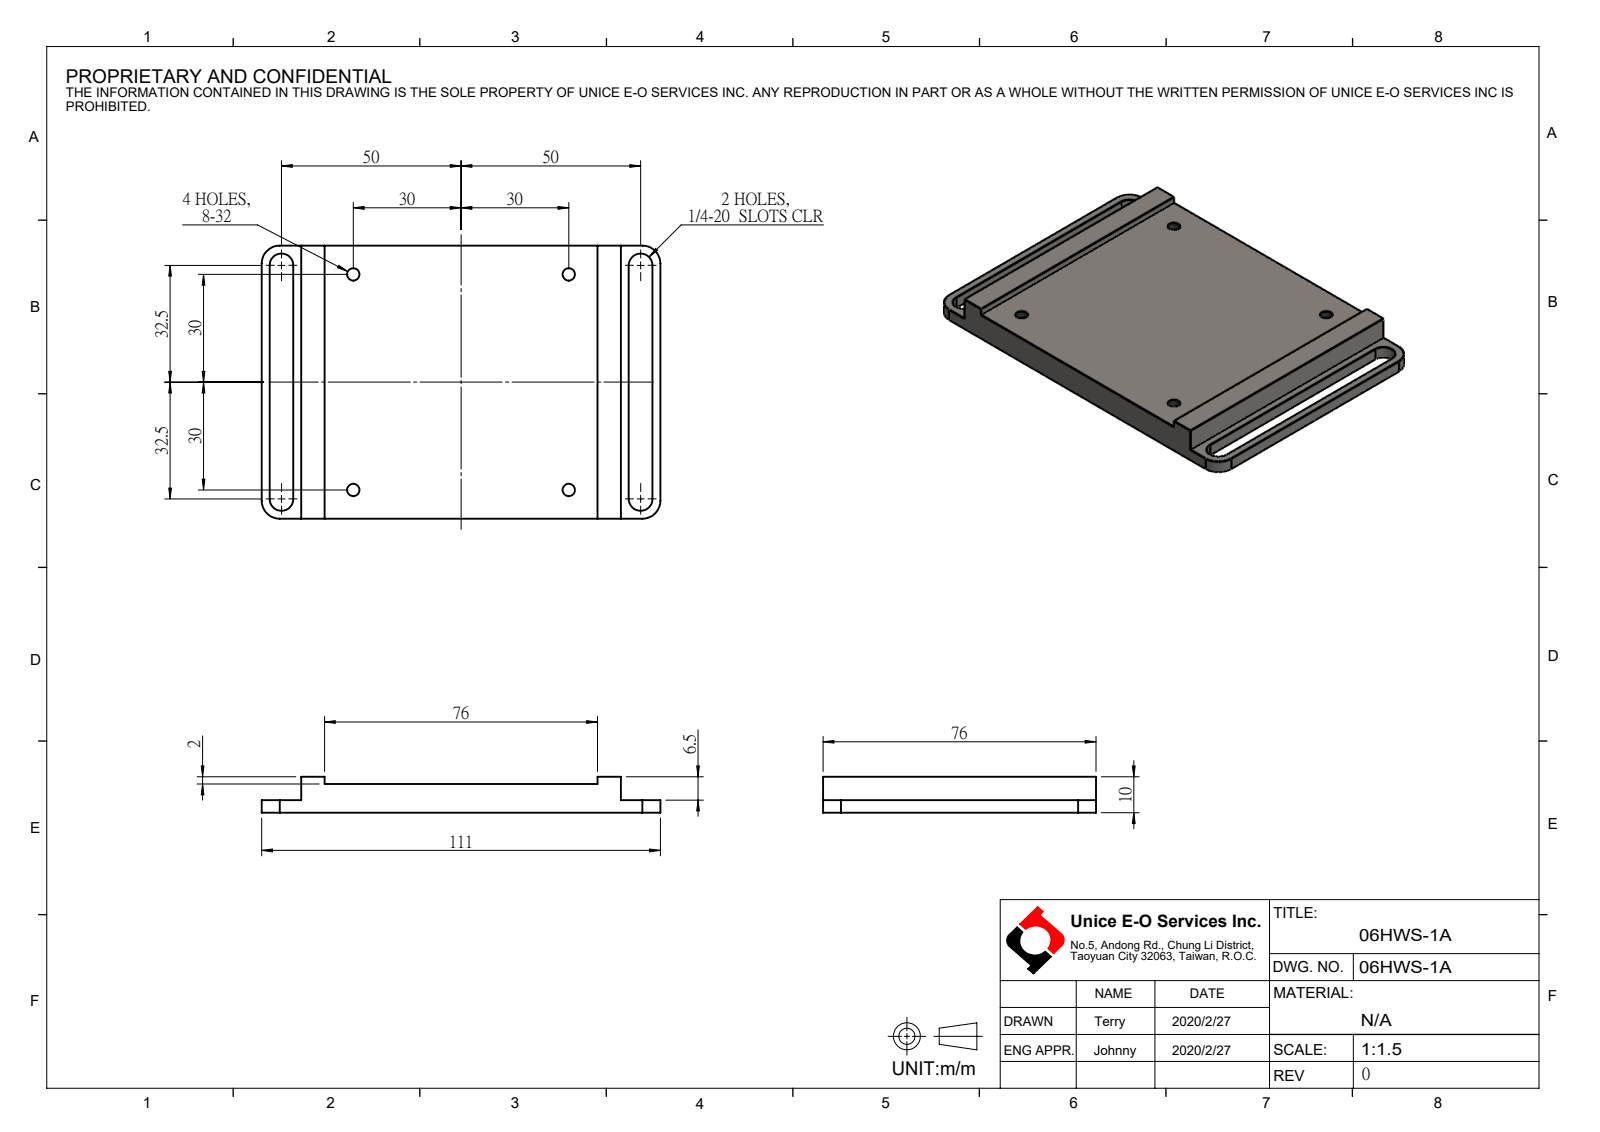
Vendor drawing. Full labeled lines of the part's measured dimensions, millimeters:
Part name (STEP PRODUCT): U-F1-06HWS1AE1-D0
STEP written by: SolidWorks 2016 (CONFIG_CONTROL_DESIGN)
Units: millimetres
Bodies: 1 solid, 34 faces (18 planar, 16 cylindrical, 0 other)
Overall size (bounding box): 111 × 76 × 10
Volume: 58 322 mm³ · Surface area: 19 728 mm²
Round holes (diameter × count): ⌀3.45 ×4
Partial cylindrical surfaces — rounded edges, fillets, slot ends (radius × count): R3.3 ×4, R5 ×4
Main face-to-face distances: 8, 6.5, 10, 2, 76, 100, 2.2, 8.8, 3.5, 4.5
Hole centre spacings: 60, 84.85
